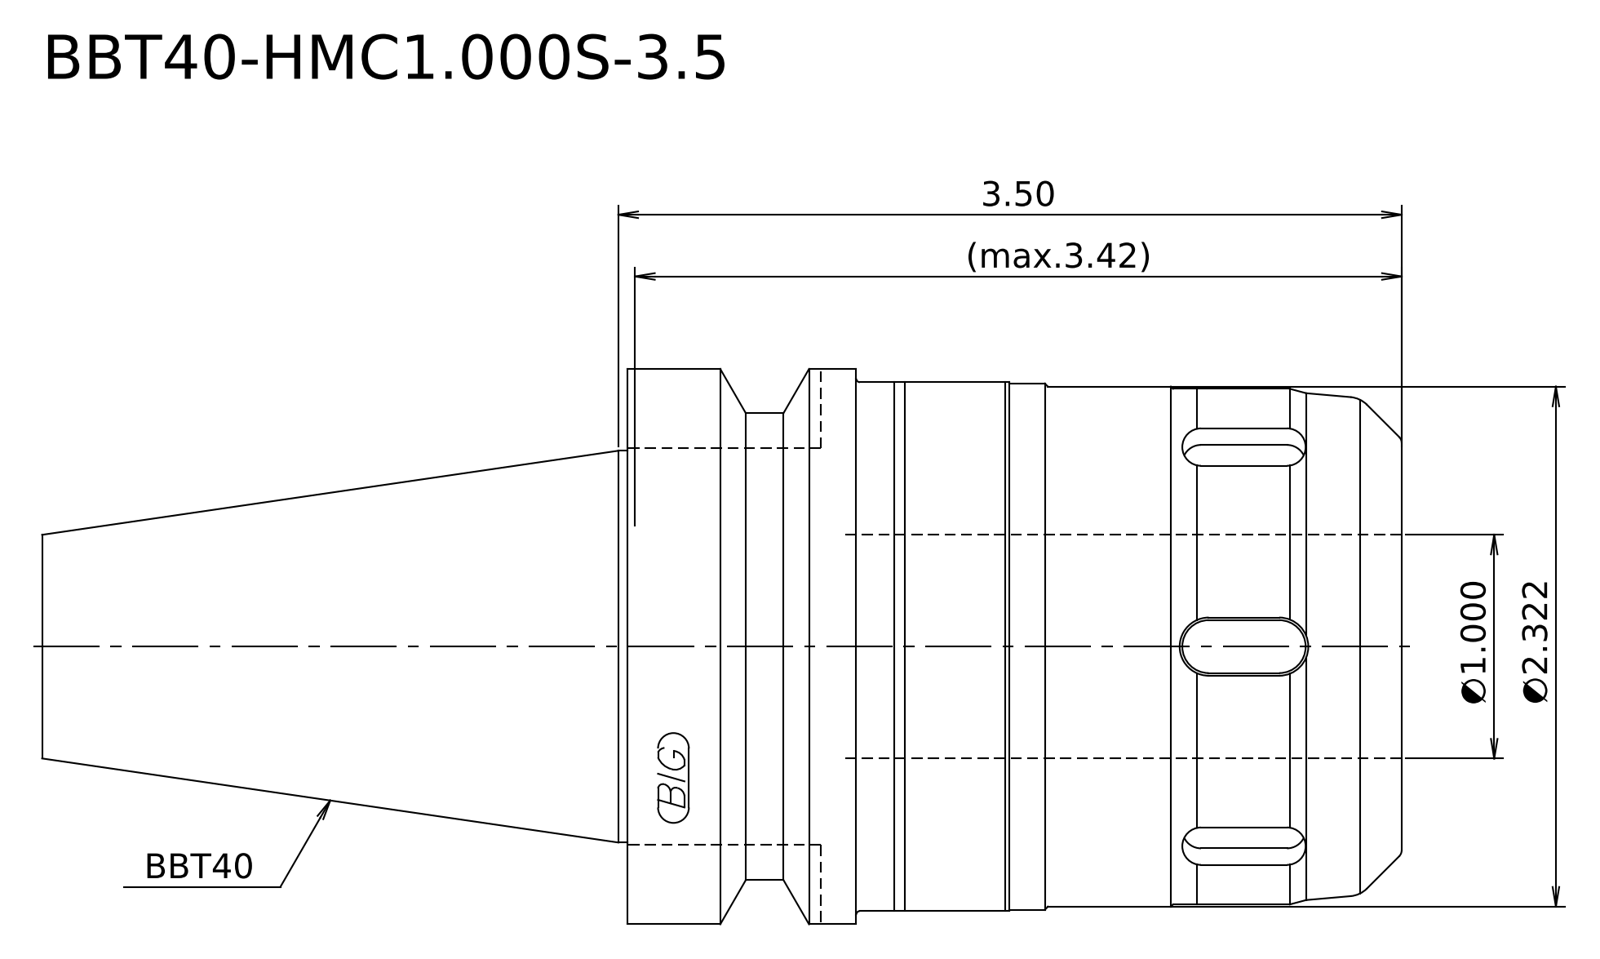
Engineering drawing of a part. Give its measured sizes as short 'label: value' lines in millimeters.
written by: Kubotek KeyCreator 2011 V10.0.2 (22737) (automotive_design)
unit: mm
bodies: 1 solid, 22 faces (5 planar, 8 cylindrical, 9 other)
size: 154.3 × 63 × 63
volume: 306 411 mm³; area: 29 184 mm²
bosses: 1× ⌀63, 1× ⌀60, 1× ⌀59.7, 1× ⌀59, 1× ⌀58.5, 1× ⌀53, 1× ⌀44.45
face distances: 87.9, 154.3, 66.4, 61.9, 26, 92.4, 44.5, 17.4, 43.4, 109.8
